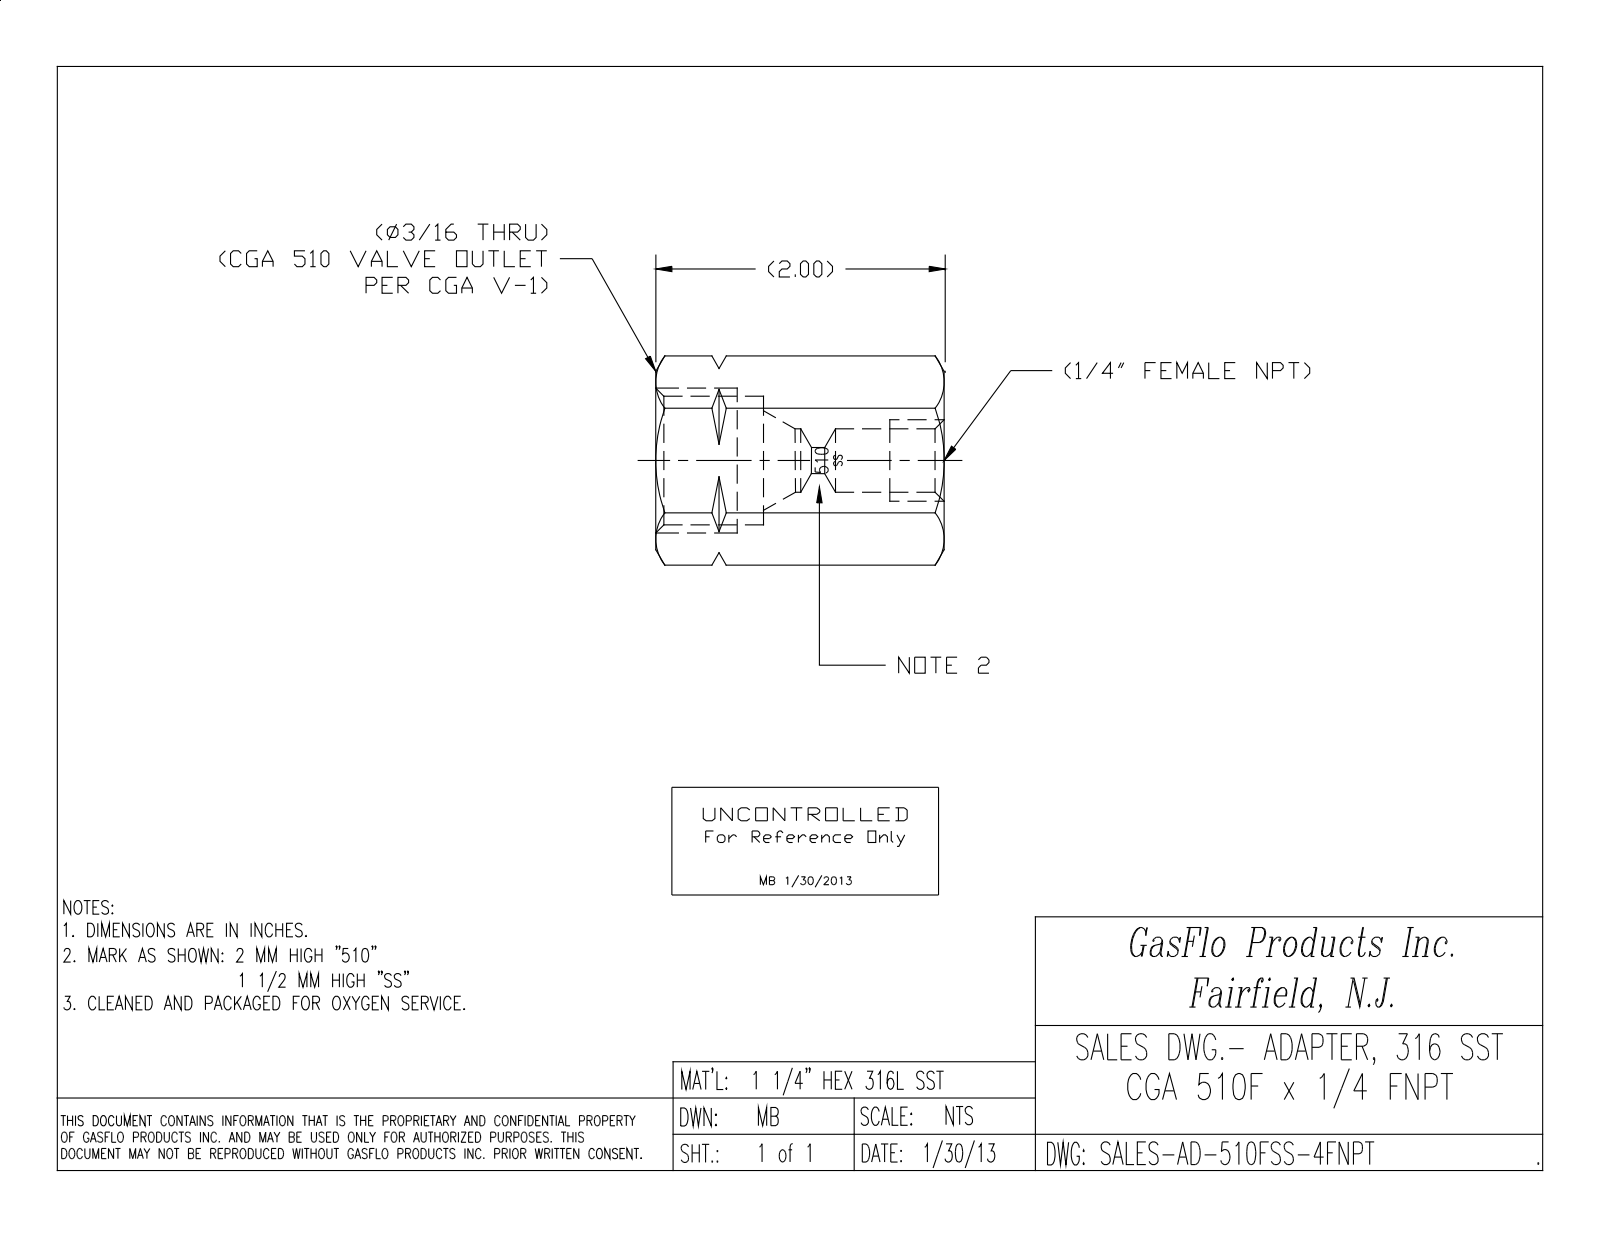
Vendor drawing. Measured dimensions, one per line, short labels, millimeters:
name: AD-510FSS-4FNPT
written by: SolidWorks 2018 (CONFIG_CONTROL_DESIGN)
unit: mm
bodies: 1 solid, 150 faces (31 planar, 25 cylindrical, 94 other)
size: 50.8 × 36.7 × 31.8
volume: 34 510 mm³; area: 10 350 mm²
holes: 1× ⌀4.7, 1× ⌀10.7, 1× ⌀10.7, 1× ⌀20.6
face distances: 31.8, 31.8, 50.8, 33.4, 17.4, 31.5, 29.9, 3.4, 20.9, 29.7
